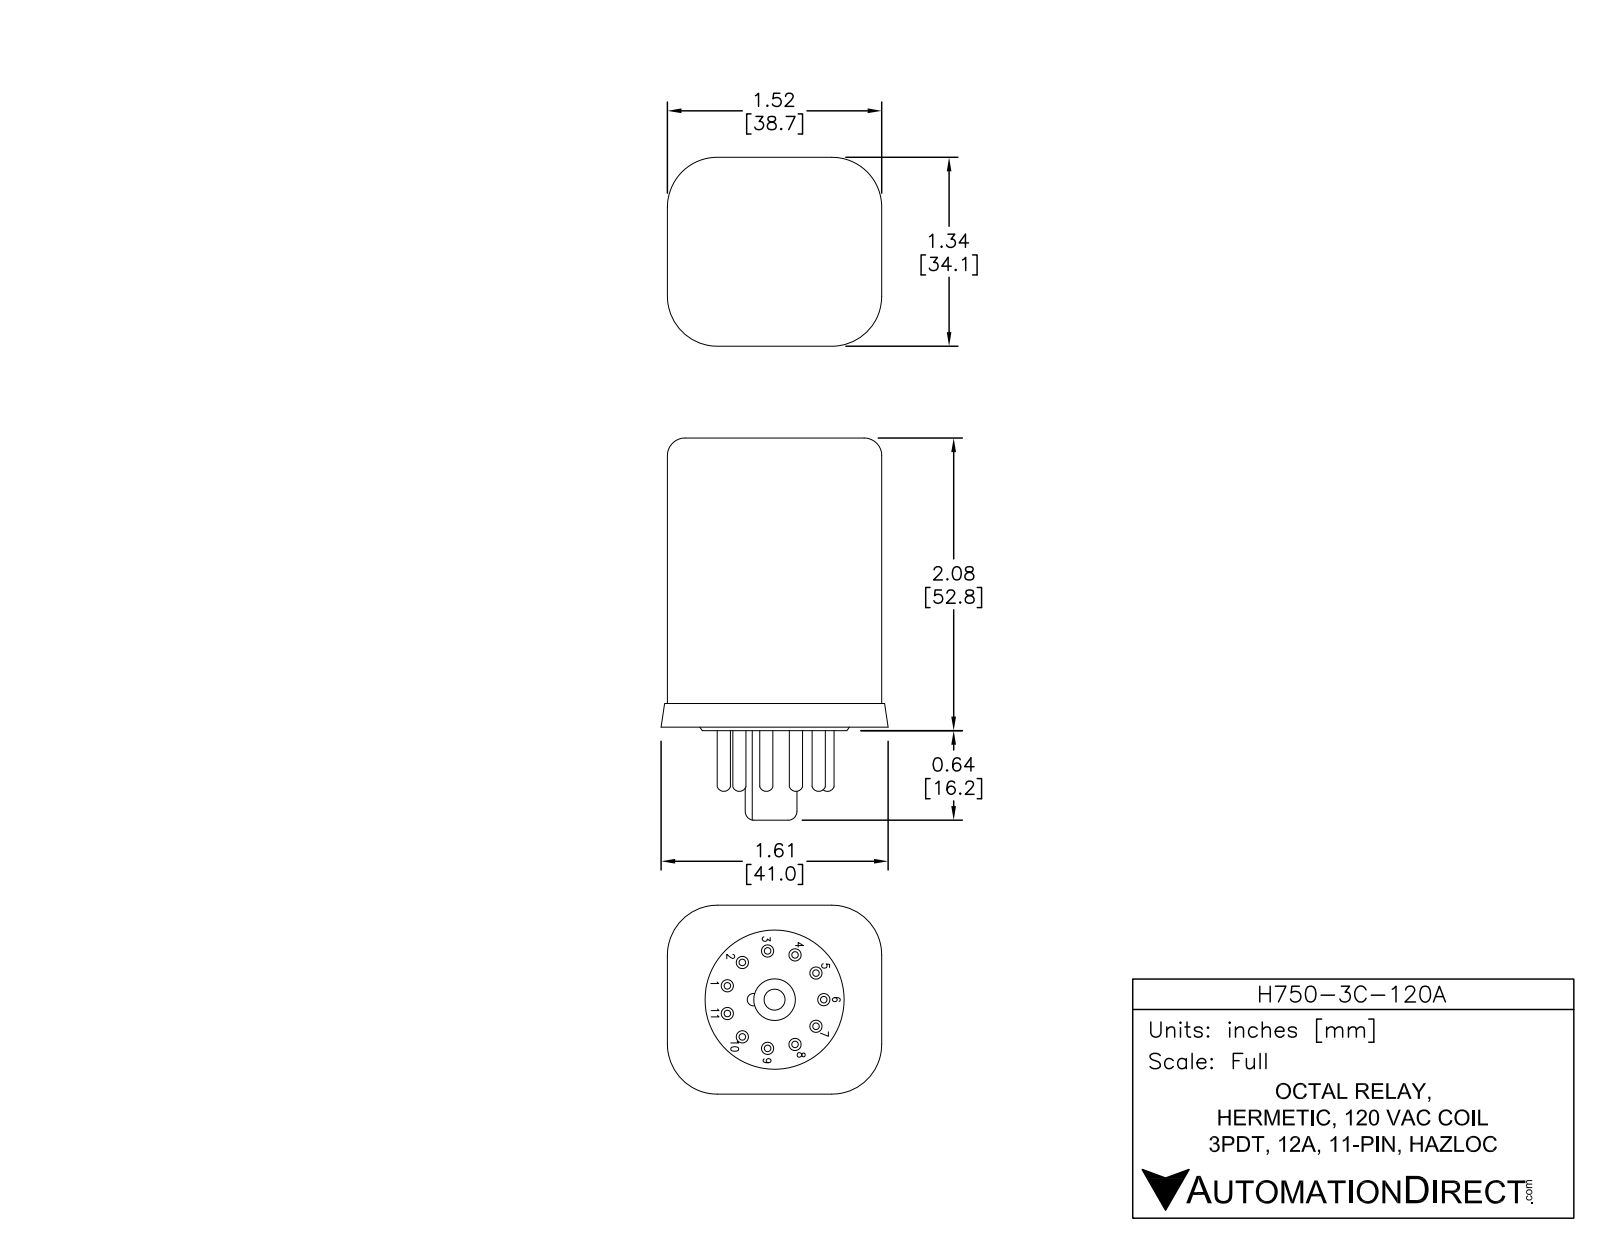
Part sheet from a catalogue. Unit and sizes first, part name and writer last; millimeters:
Units: millimetres
Overall size (bounding box): 67.3 × 41.35 × 36.6
Round holes (diameter × count): ⌀4.5 ×8, ⌀3.9 ×1
Round bosses / shafts (diameter × count): ⌀2.31 ×8, ⌀27 ×1, ⌀12 ×1, ⌀8 ×1
Partial cylindrical surfaces — rounded edges, fillets, slot ends (radius × count): R0.62 ×8, R2.5 ×4, R10 ×4, R11.3 ×4, R0.5 ×2, R0.59 ×1
Main face-to-face distances: 53, 34, 38.75, 0.5, 53.5, 1.3, 35.3, 40.05, 1, 54
Hole centre spacings: 8.5, 12.02, 15.7, 6.5, 6.51, 16.99
Volume: 66 961 mm³ · Surface area: 10 746 mm²
Bodies: 13 solids, 291 faces (123 planar, 65 cylindrical, 103 other)
Part name (STEP PRODUCT): H750-3C-120A
STEP written by: SolidWorks 2013 (AUTOMOTIVE_DESIGN)
